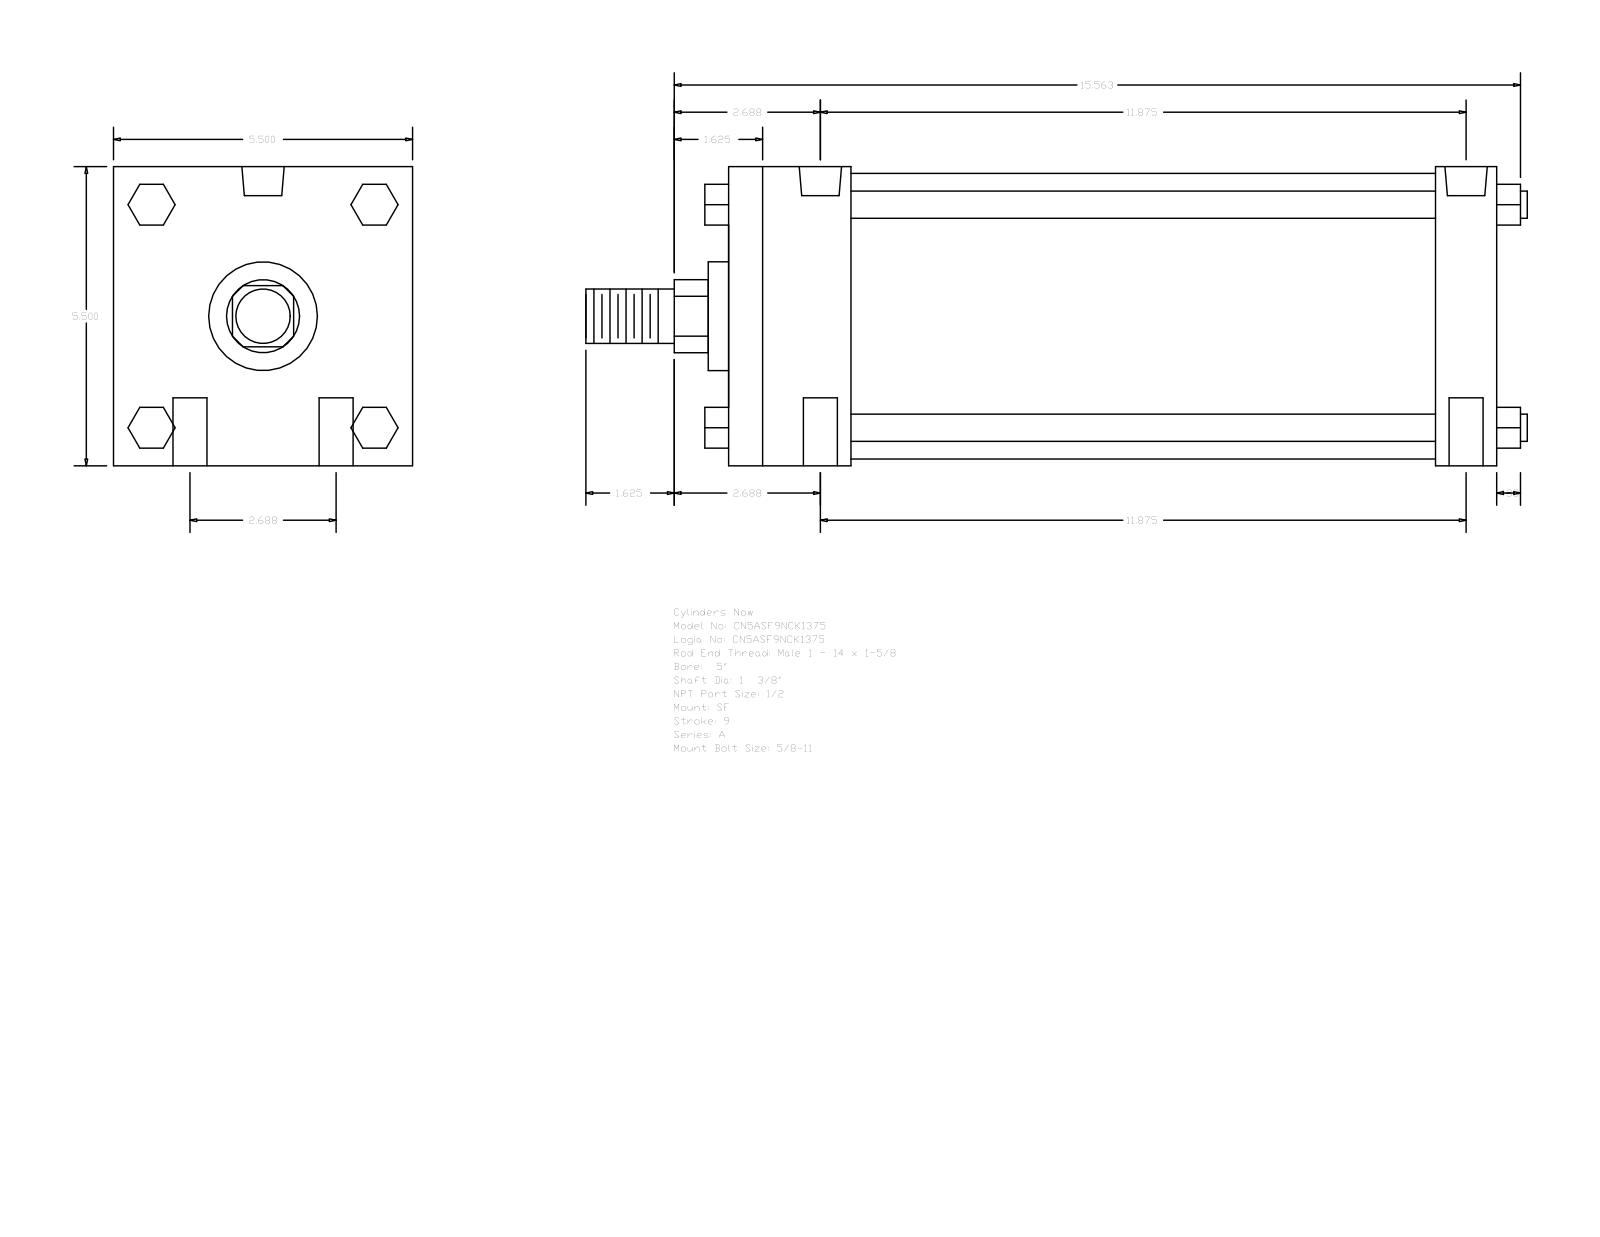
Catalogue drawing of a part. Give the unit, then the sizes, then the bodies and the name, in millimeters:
Units: millimetres
Overall size (bounding box): 439.74 × 139.7 × 139.7
Round holes (diameter × count): ⌀15.88 ×4, ⌀8.73 ×2, ⌀19.77 ×2
Round bosses / shafts (diameter × count): ⌀12.7 ×4, ⌀133.35 ×1, ⌀50.8 ×1, ⌀34.92 ×1, ⌀25.4 ×1
Partial cylindrical surfaces — rounded edges, fillets, slot ends (radius × count): R17.06 ×1
Main face-to-face distances: 139.7, 358.78, 57.15, 28.58, 330.2, 273.05, 301.63, 19.05, 52.07, 90.18
Hole centre spacings: 34.13, 303.55, 301.63, 68.26, 309.26, 296.85
Bodies: 0 solids, 124 faces (94 planar, 30 cylindrical, 0 other)
Part name (STEP PRODUCT): A_SF__0500_1.375
STEP written by: GSSL Pune (CONFIG_CONTROL_DESIGN)
